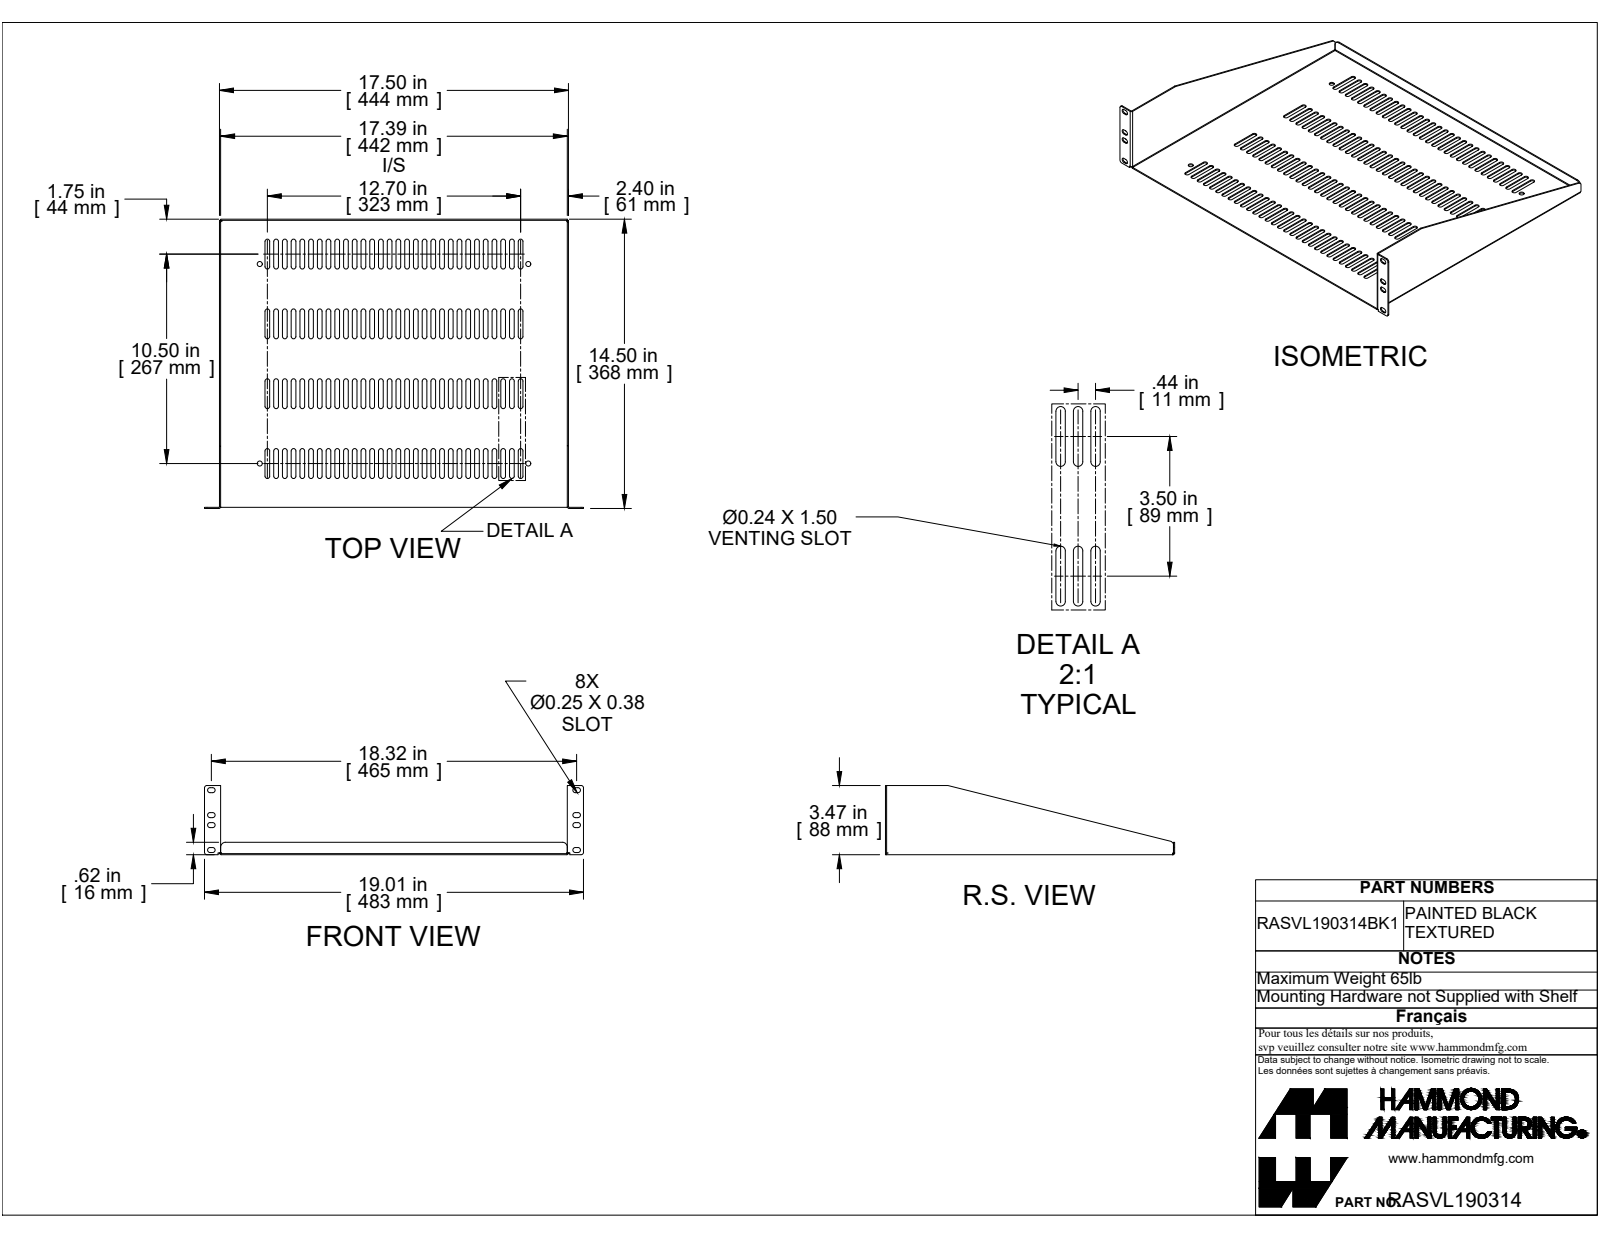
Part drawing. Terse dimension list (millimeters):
name: RASVL190314BK1
written by: SolidWorks 2019 (CONFIG_CONTROL_DESIGN)
unit: mm
bodies: 0 solids, 582 faces (298 planar, 280 cylindrical, 4 other)
size: 482.8 × 368.3 × 88.1
bosses: 4× ⌀6.4
rounds: 228× R3, 20× R3.2, 12× R3, 5× R0.7, 5× R2.2, 3× R1.4, 2× R6.4
face distances: 1.4, 443.1, 441.6, 444.5, 365.4, 366.9, 1.4, 366.9, 368.3, 22.3
